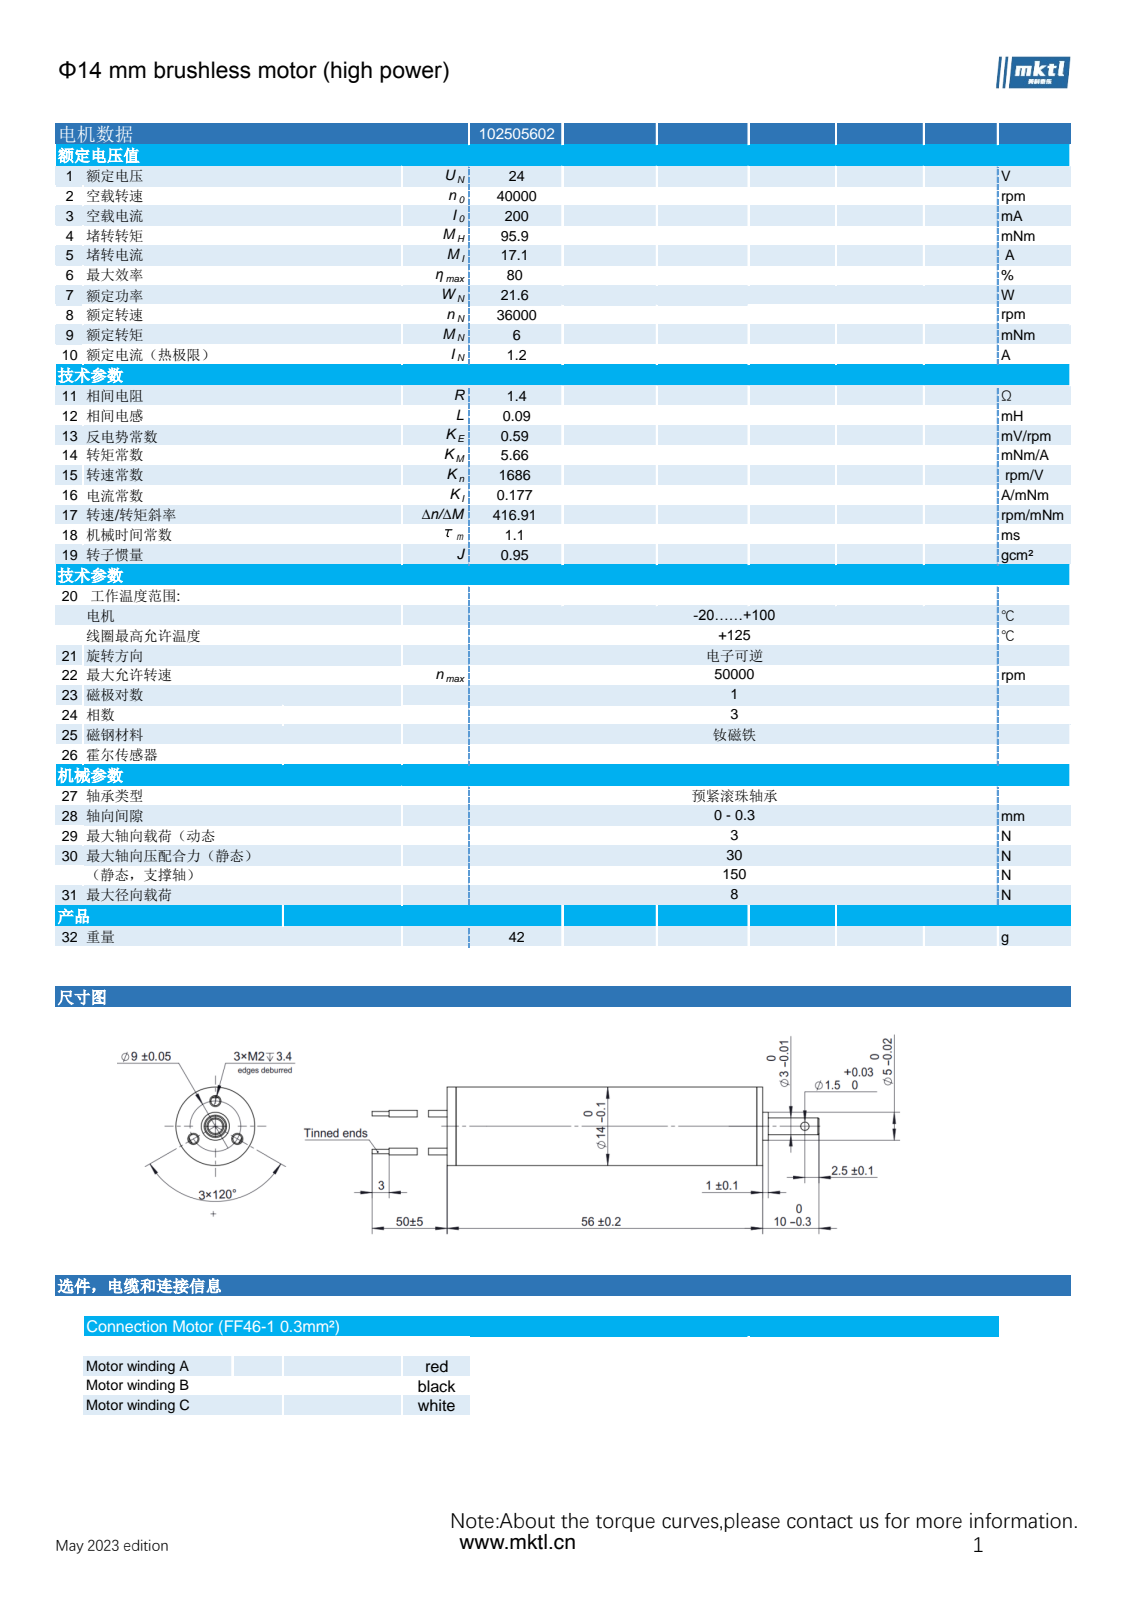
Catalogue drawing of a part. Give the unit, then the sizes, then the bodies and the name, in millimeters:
Units: millimetres
Overall size (bounding box): 79.3 × 14 × 14
Round holes (diameter × count): ⌀1.5 ×4, ⌀1.6 ×3, ⌀3 ×1, ⌀3.1 ×1, ⌀4 ×1, ⌀5.2 ×1, ⌀6 ×1, ⌀7 ×1, ⌀7.1 ×1, ⌀9.8 ×1, ⌀10 ×1, ⌀10.2 ×1
Round bosses / shafts (diameter × count): ⌀1.2 ×3, ⌀0.8 ×3, ⌀0.58 ×3, ⌀14 ×1, ⌀13.2 ×1, ⌀13.1 ×1, ⌀6.6 ×1, ⌀6.4 ×1
Main face-to-face distances: 0.4, 0.6, 0.8, 1, 1.2, 1.4, 1.6, 1.8, 2, 2.2
Hole centre spacings: 4.5, 7.8, 9
Volume: 8 004 mm³ · Surface area: 41 917 mm²
Bodies: 240 solids, 1549 faces (505 planar, 996 cylindrical, 48 other)
Part name (STEP PRODUCT): 102505602
STEP written by: SolidWorks 2025 (AUTOMOTIVE_DESIGN)
